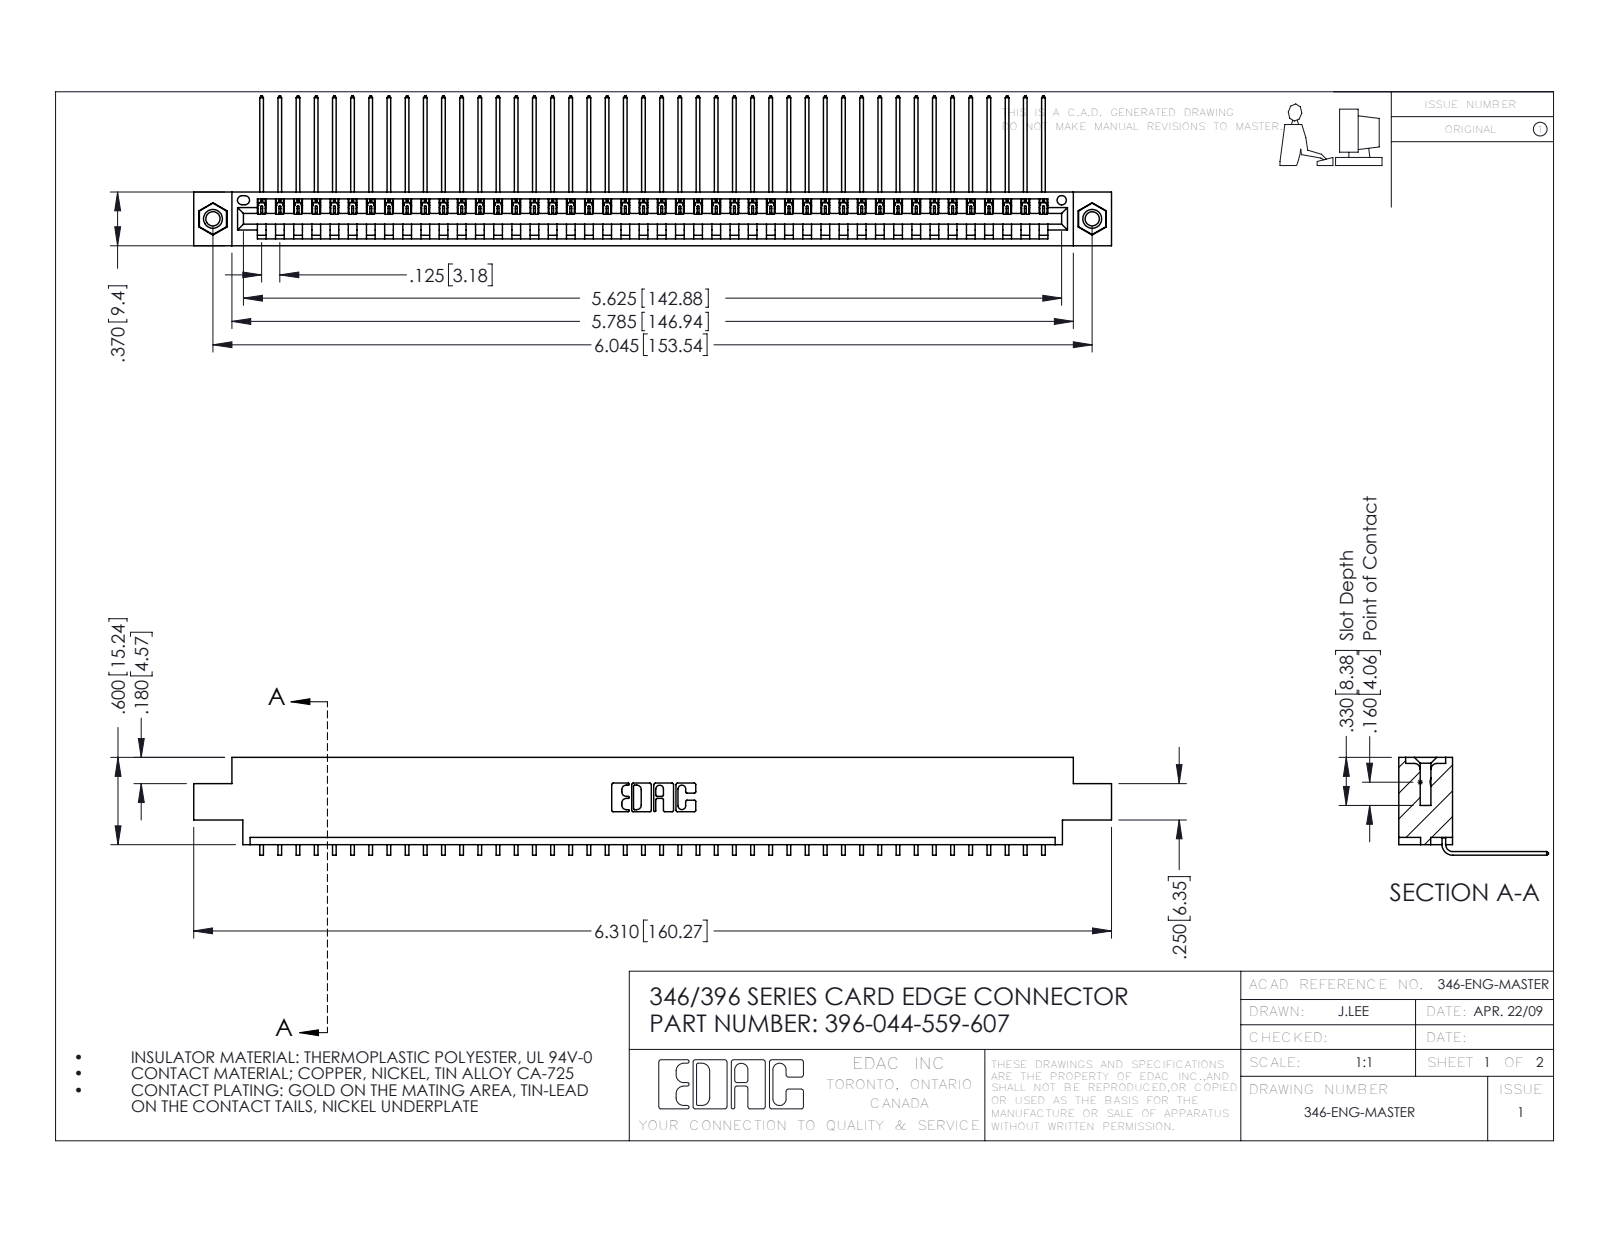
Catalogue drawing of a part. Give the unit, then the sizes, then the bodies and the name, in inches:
Units: inches
Overall size (bounding box): 6.31 × 1.03 × 0.673
Round holes (diameter × count): ⌀0.098 ×2, ⌀0.125 ×2, ⌀0.156 ×2, ⌀0.064 ×1
Round bosses / shafts (diameter × count): ⌀0.155 ×2
Partial cylindrical surfaces — rounded edges, fillets, slot ends (radius × count): R0.006 ×88, R0.01 ×22, R0.007 ×6, R0.031 ×6, R0.026 ×3, R0.031 ×2, R0.04 ×2, R0.014 ×1
Main face-to-face distances: 0.048, 0.322, 0.37, 0.025, 0.25, 0.072, 0.222, 0.148, 0.298, 0.1
Hole centre spacings: 0.246, 5.836, 6.045
Volume: 0.936 in³ · Surface area: 31.4 in²
Bodies: 47 solids, 2826 faces (1960 planar, 850 cylindrical, 16 other)
Part name (STEP PRODUCT): 345-250-001_345-250-005-103; 396-044-559-607; 346 Part_0.170 Offset - 0.156 Dia-TI; 345-292-001_558 559 Tail - 1
STEP written by: SolidWorks 2016 (CONFIG_CONTROL_DESIGN)
